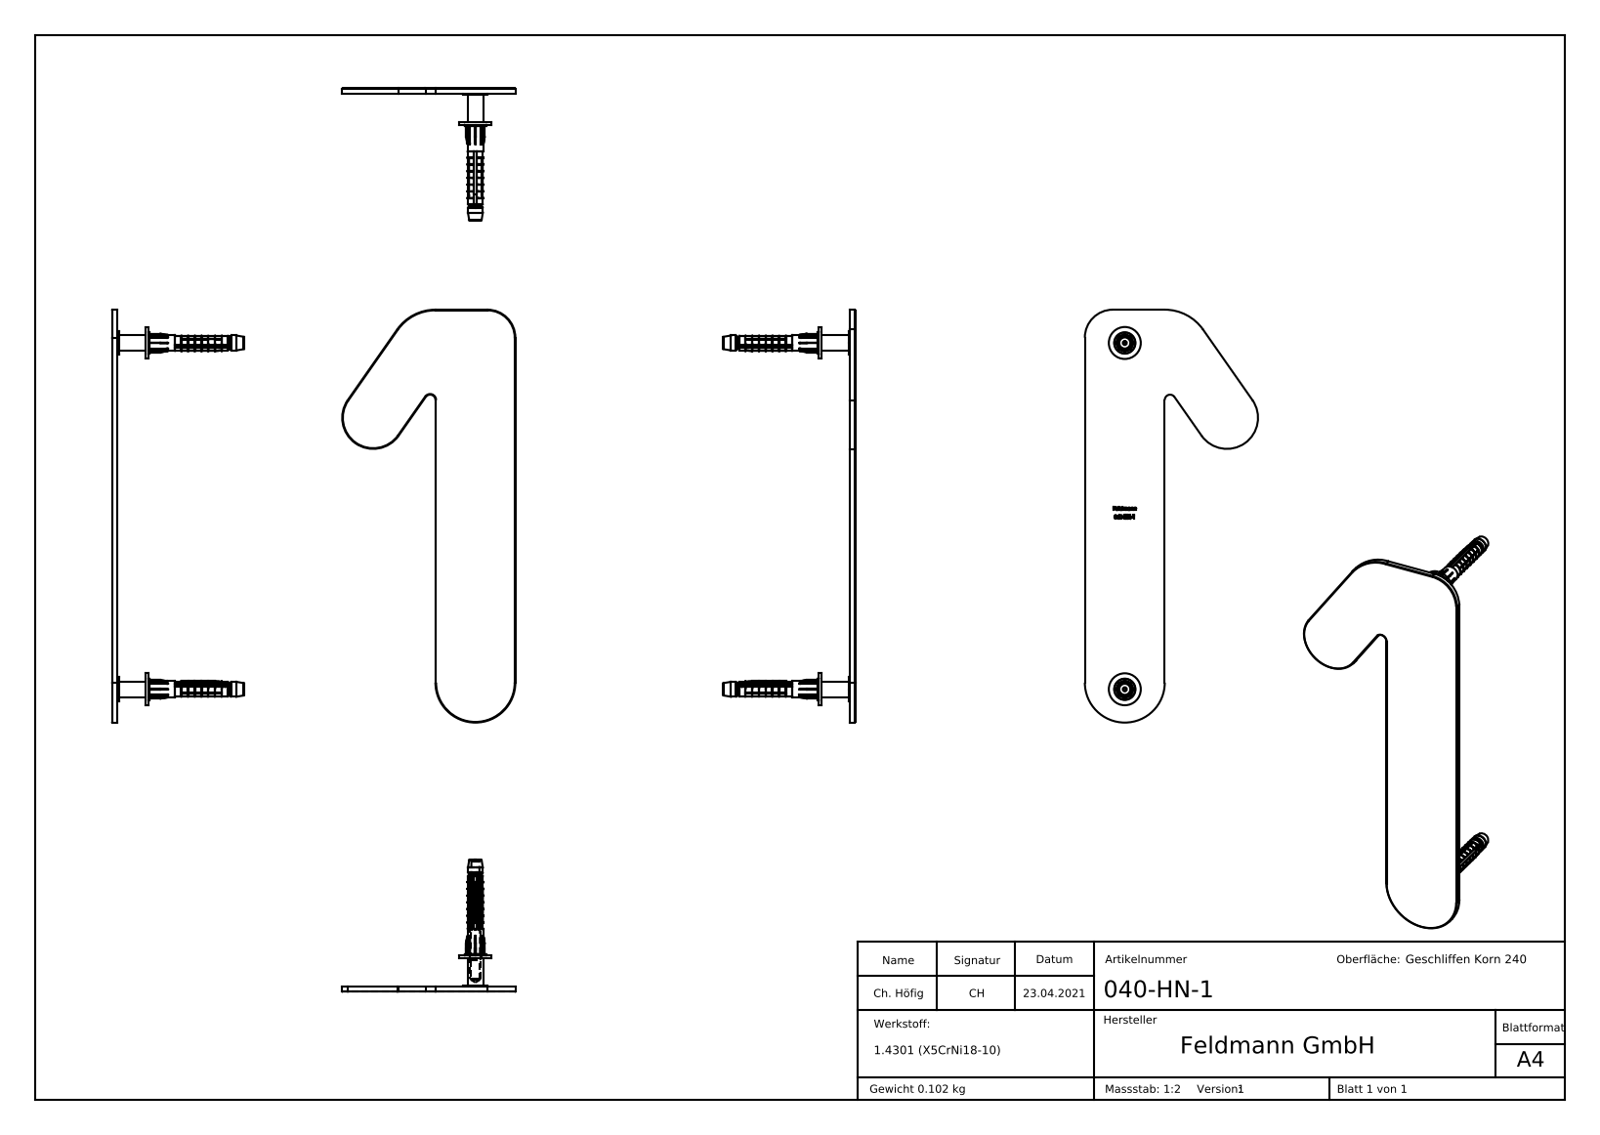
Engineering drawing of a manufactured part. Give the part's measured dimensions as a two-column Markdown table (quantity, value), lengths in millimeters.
| quantity | value |
| --- | --- |
| part name | 040-HN-X Teil3_040-HN-X Teil3; 040-HN-X Teil2_040-HN-X Teil2; 040-HN-1; 040-HN-X Teil3 (+5 more) |
| STEP written by | SolidWorks 2018 (CONFIG_CONTROL_DESIGN) |
| units | millimeters |
| bodies | 7 solids, 1548 faces (362 planar, 389 cylindrical, 797 other) |
| overall size | 10000 × 5217.43 × 4607.88 |
| volume | 13 933 mm³ |
| surface area | 16 475 mm² |
| round holes (diameter × count) | 3.3 × 2, 4.3 × 2 |
| round bosses / shafts (diameter × count) | 12 × 2, 9 × 2, 8 × 2, 6 × 2, 5.8 × 2, 5.6 × 2, 4.6 × 2, 4 × 2 |
| partial cylindrical surfaces (radius × count) | 0.1 × 22, 0.25 × 5, 3.5 × 2, 2 × 1, 10.5 × 1, 11.65 × 1, 15 × 1, 17.57 × 1 |
| main face-to-face distances | 2, 11.6, 13.6, 1.1, 10.5, 12.5, 30, 0.5, 2.5, 10 |
| hole center spacings | 130 |
